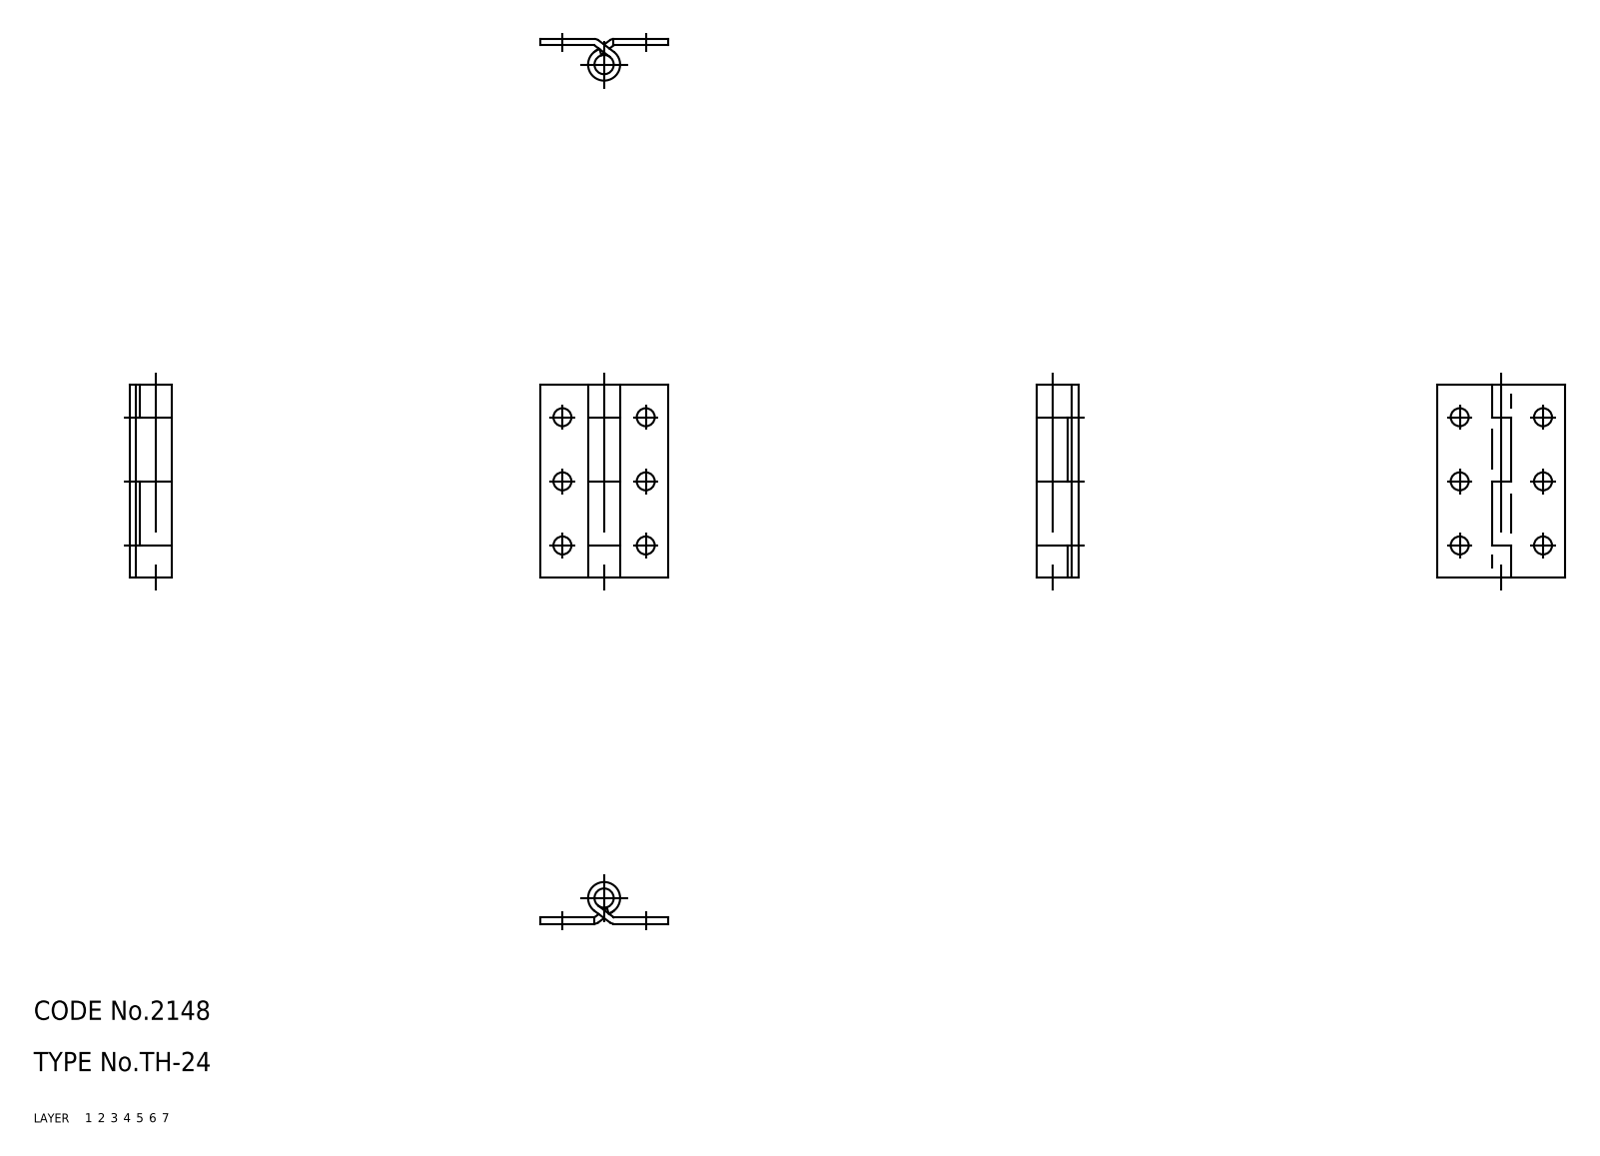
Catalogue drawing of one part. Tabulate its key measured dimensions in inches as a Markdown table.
| quantity | value |
| --- | --- |
| part name | shaft; hinge piece_B; hinge piece_A; TH_24_6489_36 |
| STEP written by | CADfix (AUTOMOTIVE_DESIGN) |
| units | inches |
| bodies | 3 solids, 60 faces (0 planar, 0 cylindrical, 60 other) |
| overall size | 1.181 × 0.787 × 0.256 |
| volume | 0.067 in³ |
| surface area | 3.722 in² |
